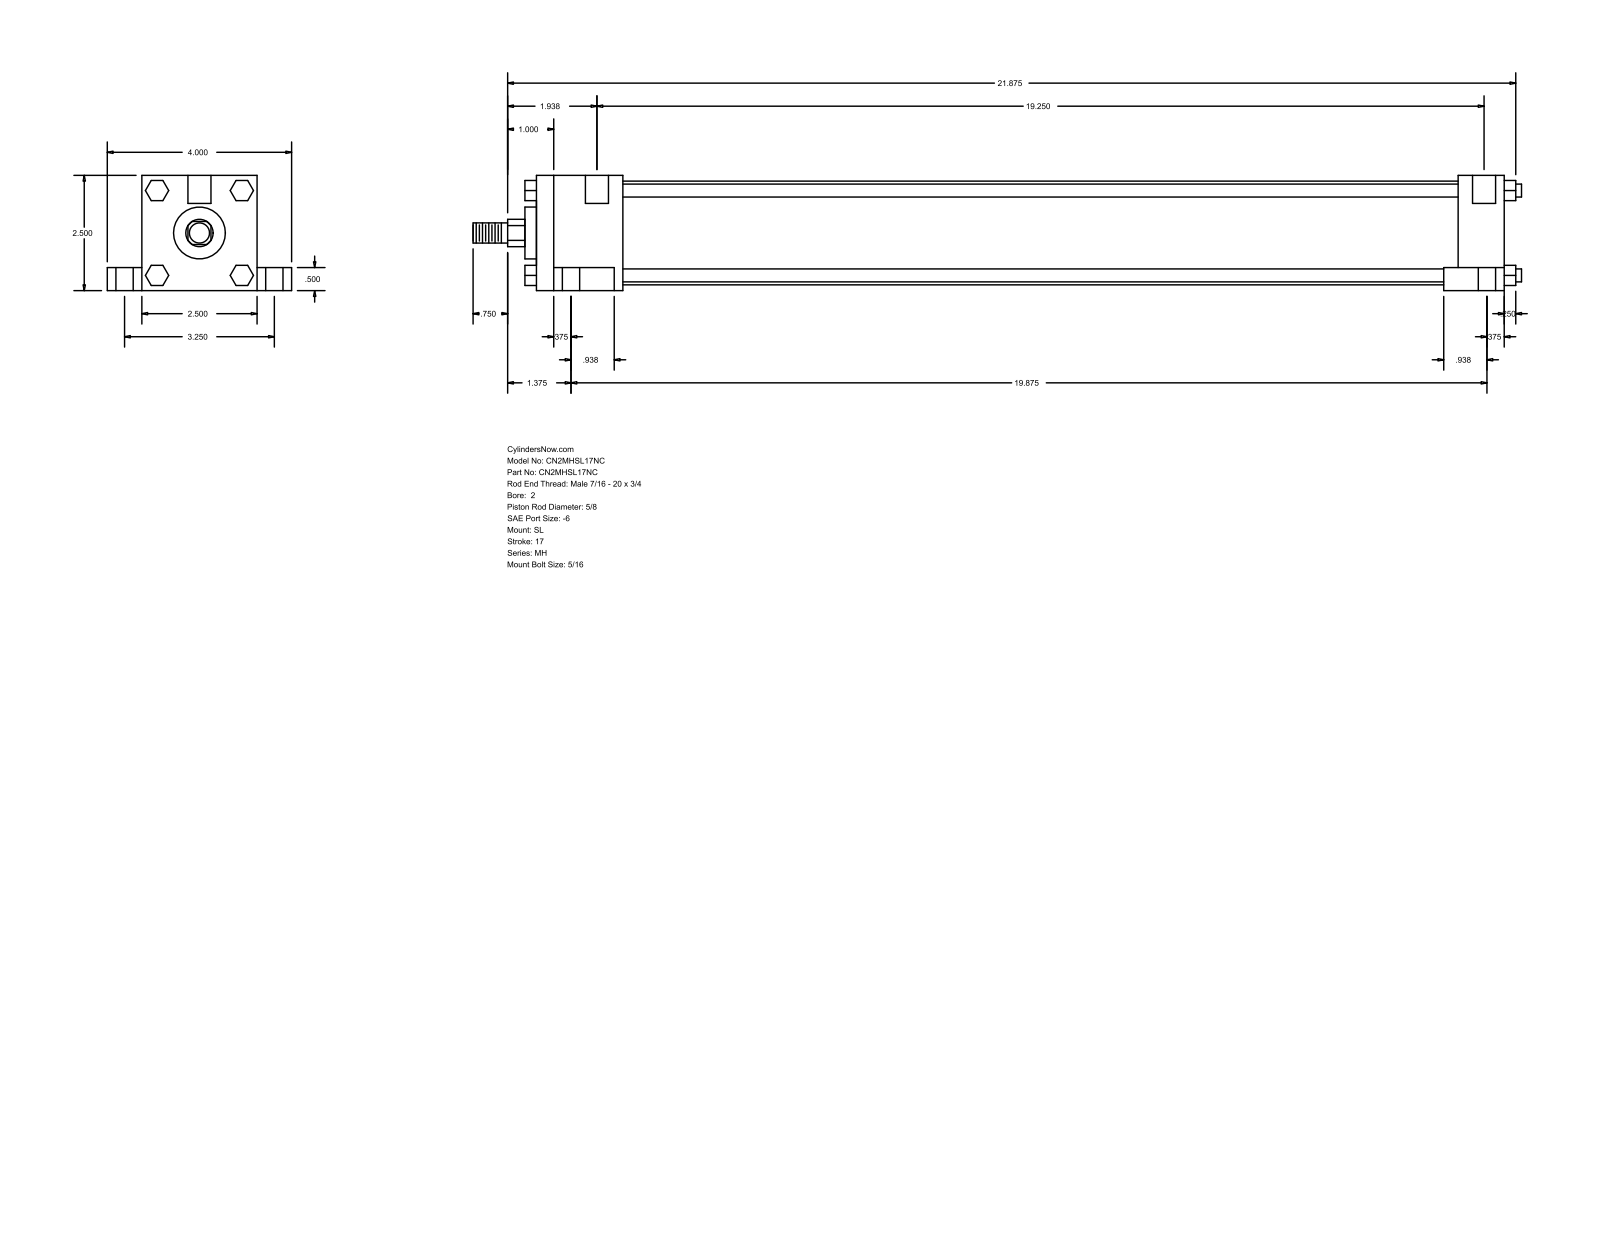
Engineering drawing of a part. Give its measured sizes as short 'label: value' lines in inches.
name: MH_SL__0200_0.625
written by: GSSL Pune (CONFIG_CONTROL_DESIGN)
unit: in
bodies: 0 solids, 148 faces (112 planar, 36 cylindrical, 0 other)
size: 22.75 × 4 × 2.5
holes: 4× ⌀0.219, 4× ⌀0.375, 4× ⌀0.625, 2× ⌀0.5
bosses: 4× ⌀0.281, 1× ⌀2.25, 1× ⌀1.125, 1× ⌀0.625, 1× ⌀0.437
rounds: 1× R0.297
face distances: 2.5, 21, 0.5, 0.75, 3.25, 2, 20, 1, 1.875, 18.125
hole spacings: 1.626, 1.668, 1.719, 3.25, 19.381, 19.563, 19.568, 19.875
